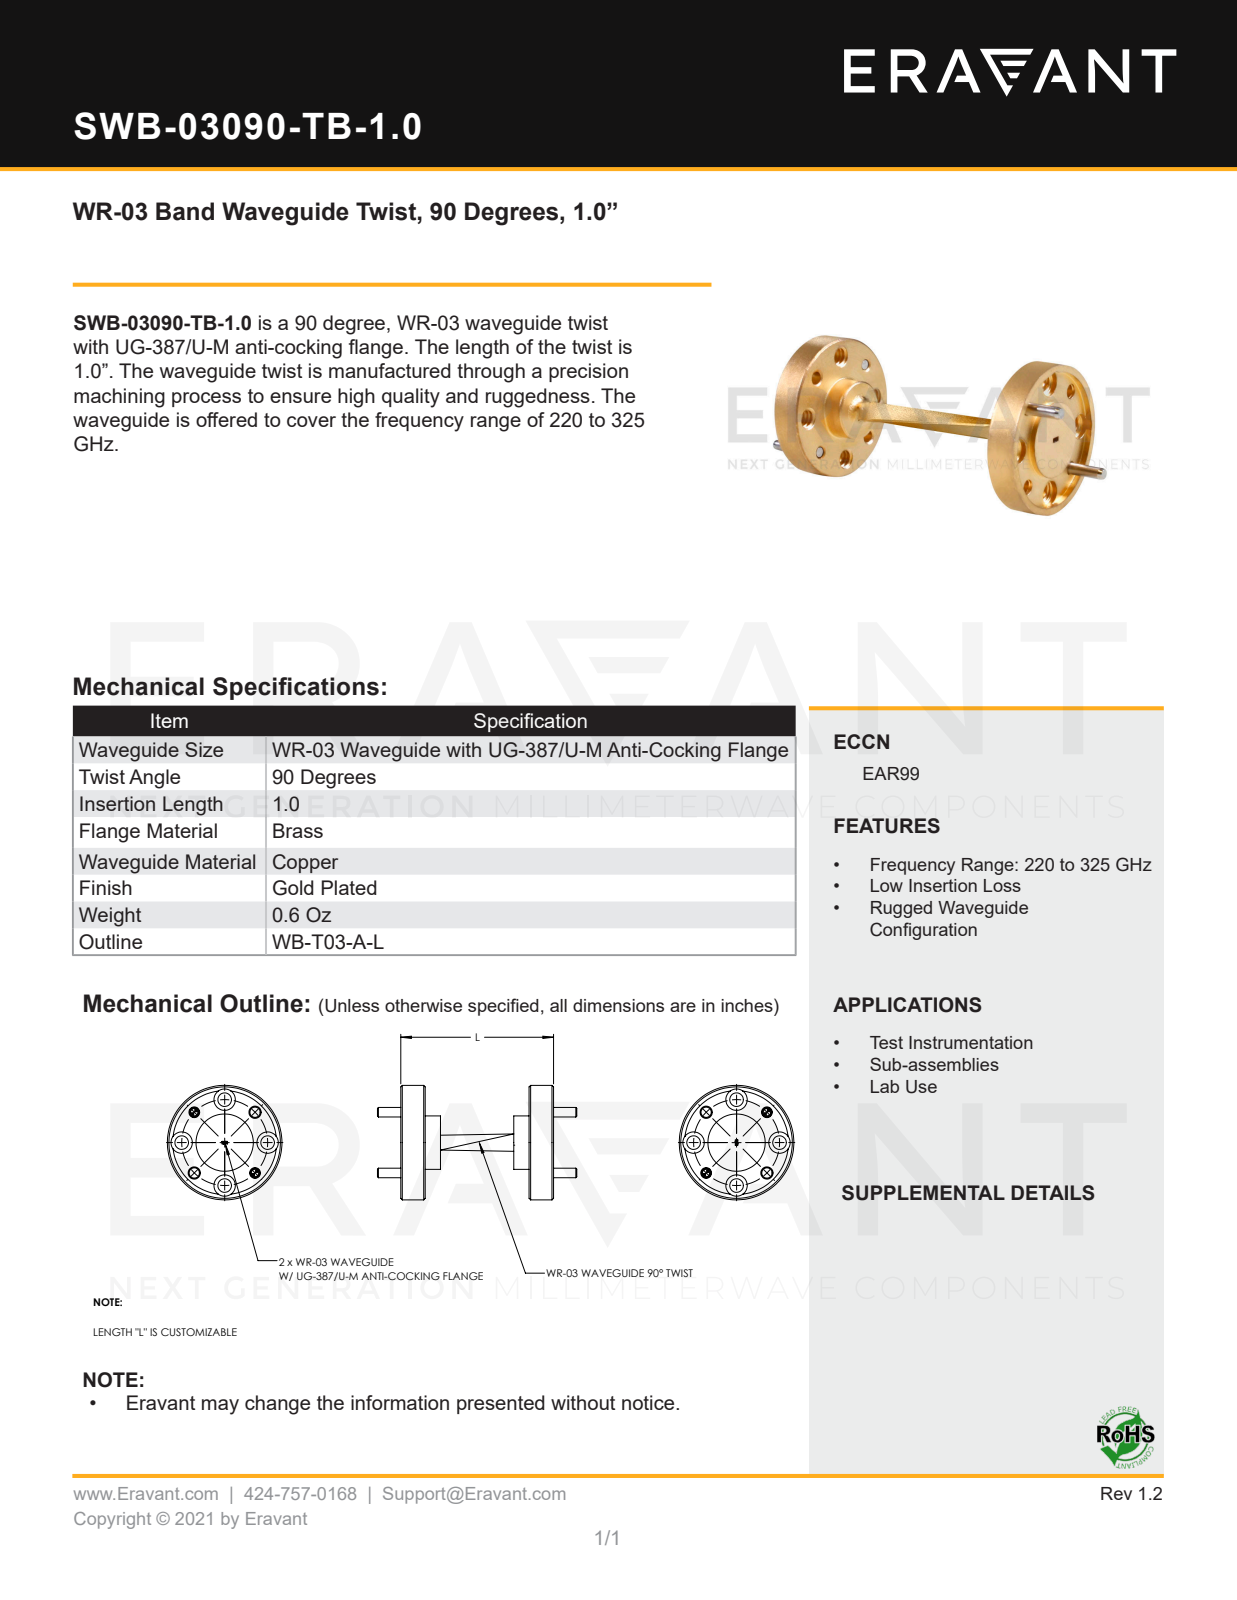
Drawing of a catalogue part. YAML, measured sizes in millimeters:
part_name: "PHW-DPXXXX-Y_PHW-DP0631-W; WB-T03-A-L, DF_SWB-03090-TB-1.0; SWB-03090-TB-1.0"
step_written_by: "SolidWorks 2021 (CONFIG_CONTROL_DESIGN)"
units: millimeters
bodies: {solids: 5, faces: 156, planar: 36, cylindrical: 76, other: 44}
overall_size: [33.1, 19.1, 19.1]
volume: 2360
surface_area: 2363
round_holes:
  - {diameter: 2.3, count: 4}
  - {diameter: 3.6, count: 4}
  - {diameter: 1.5, count: 2}
  - {diameter: 1.7, count: 2}
  - {diameter: 17.3, count: 1}
round_bosses_or_shafts:
  - {diameter: 1.6, count: 2}
  - {diameter: 19.1, count: 1}
  - {diameter: 9.5, count: 1}
  - {diameter: 8.9, count: 1}
face_to_face_distances: [17.3, 3.6, 20.8, 2.5, 24.4, 6.1, 18.3, 14.7, 24.9, 0.5]
hole_center_spacings: [5.5, 13.2, 10.1, 7.1, 7.1, 14.3, 10.1, 5.5]
